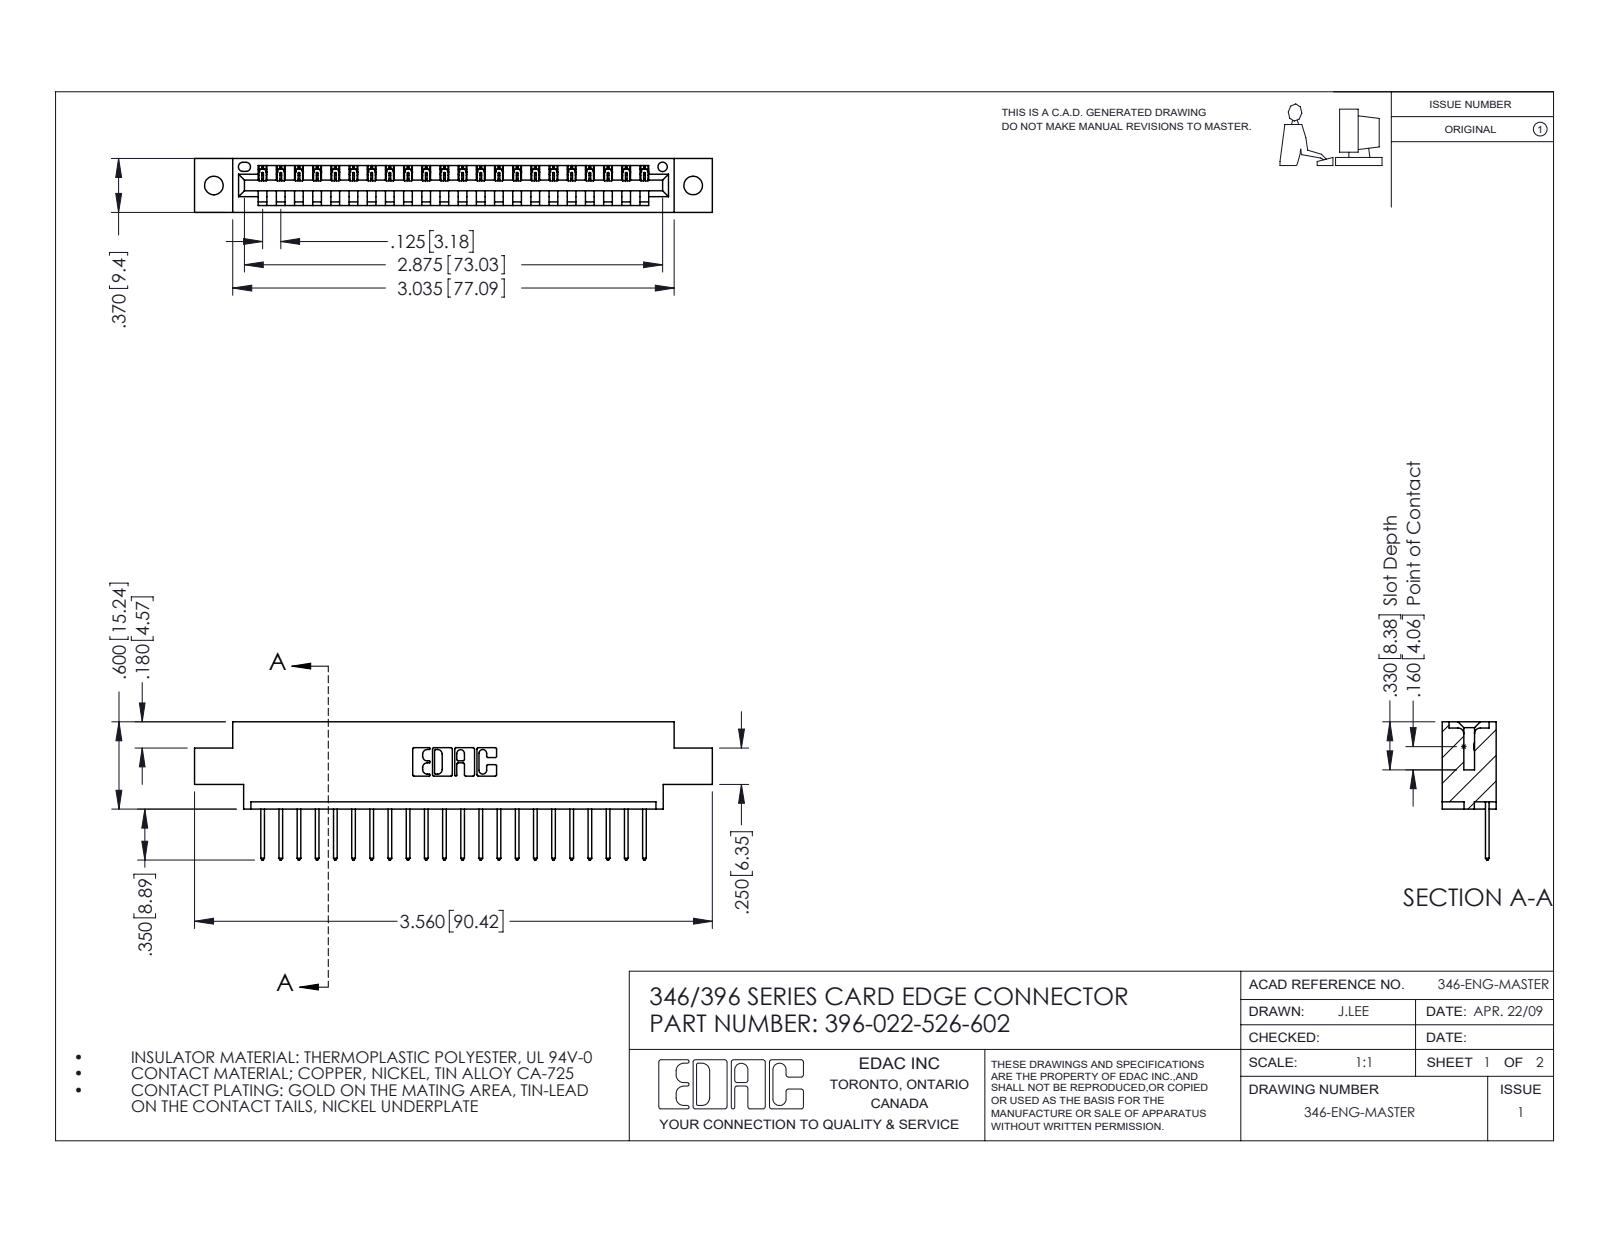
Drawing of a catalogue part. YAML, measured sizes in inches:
part_name: "345-292-001_345-293-126; 396-022-526-602; 346 Part_0.170 Offset - 0.128 Dia"
step_written_by: "SolidWorks 2016 (CONFIG_CONTROL_DESIGN)"
units: inches
bodies: {solids: 23, faces: 1402, planar: 960, cylindrical: 442, other: 0}
overall_size: [3.56, 0.95, 0.37]
volume: 0.507
surface_area: 15.56
round_holes:
  - {diameter: 0.128, count: 2}
  - {diameter: 0.064, count: 1}
partial_cylinders:
  - {radius: 0.006, count: 44}
  - {radius: 0.01, count: 44}
  - {radius: 0.01, count: 22}
  - {radius: 0.007, count: 6}
  - {radius: 0.031, count: 6}
  - {radius: 0.026, count: 3}
  - {radius: 0.031, count: 2}
  - {radius: 0.04, count: 2}
face_to_face_distances: [0.048, 0.322, 0.37, 0.25, 0.072, 0.298, 0.025, 0.148, 0.222, 0.1]
hole_center_spacings: [0.246, 3.087, 3.295]
